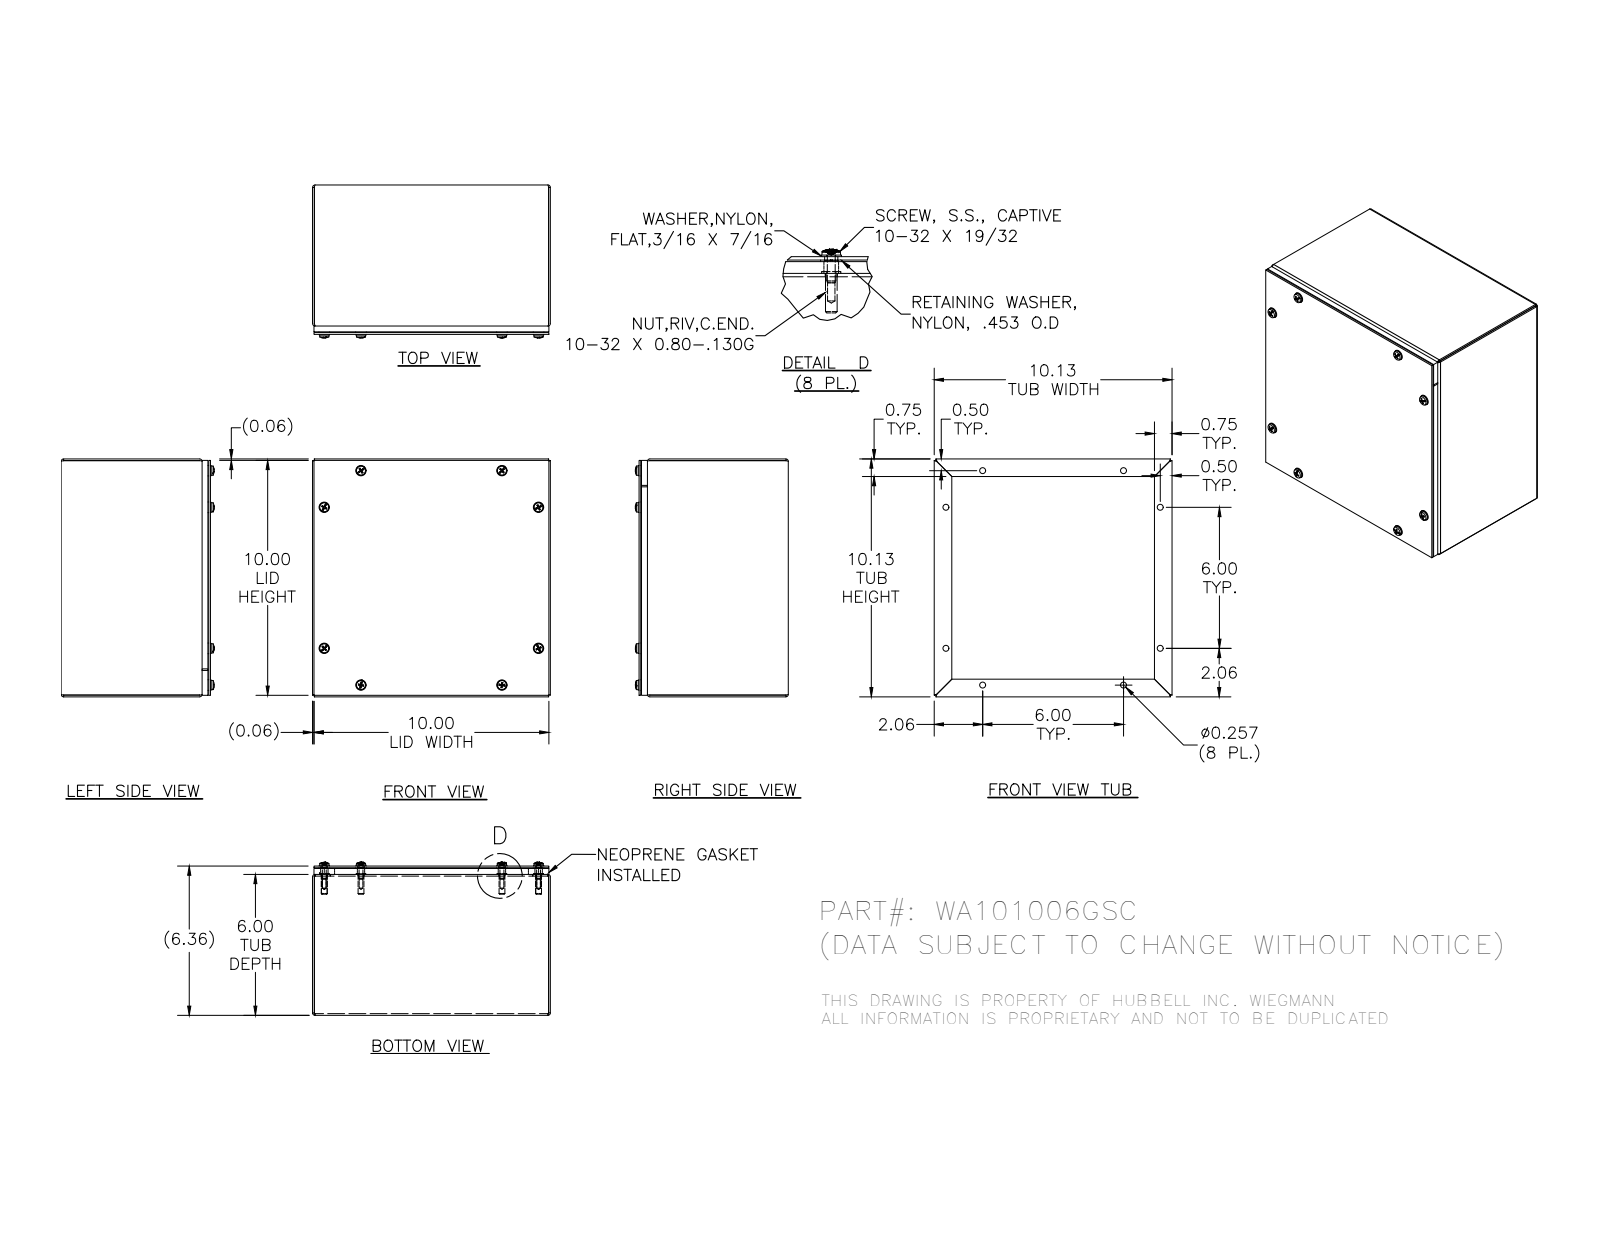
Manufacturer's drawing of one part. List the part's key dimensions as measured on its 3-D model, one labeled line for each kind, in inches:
Part name (STEP PRODUCT): WA1010GSC_LP; 39035; WA101006GSCBKP; 34984 (+4 more)
STEP written by: SolidWorks 2014 (AUTOMOTIVE_DESIGN)
Units: inches
Bodies: 36 solids, 892 faces (420 planar, 240 cylindrical, 232 other)
Overall size (bounding box): 10.125 × 10.125 × 6.511
Volume: 42.46 in³ · Surface area: 1 038 in²
Round holes (diameter × count): ⌀0.156 ×8, ⌀0.188 ×8, ⌀0.196 ×8, ⌀0.257 ×8, ⌀0.278 ×8, ⌀0.281 ×8, ⌀0.313 ×8
Round bosses / shafts (diameter × count): ⌀0.453 ×8, ⌀0.437 ×8, ⌀0.406 ×8, ⌀0.248 ×8, ⌀0.167 ×8
Partial cylindrical surfaces — rounded edges, fillets, slot ends (radius × count): R0.031 ×8, R0.089 ×8, R0.105 ×8
Main face-to-face distances: 0.074, 10.051, 6.282, 10.125, 9.977, 6.356, 6.208, 0.356, 5.926, 0.282
Hole centre spacings: 6, 7.722, 7.722, 2.209, 7.722, 10.921, 10.694, 2.21
